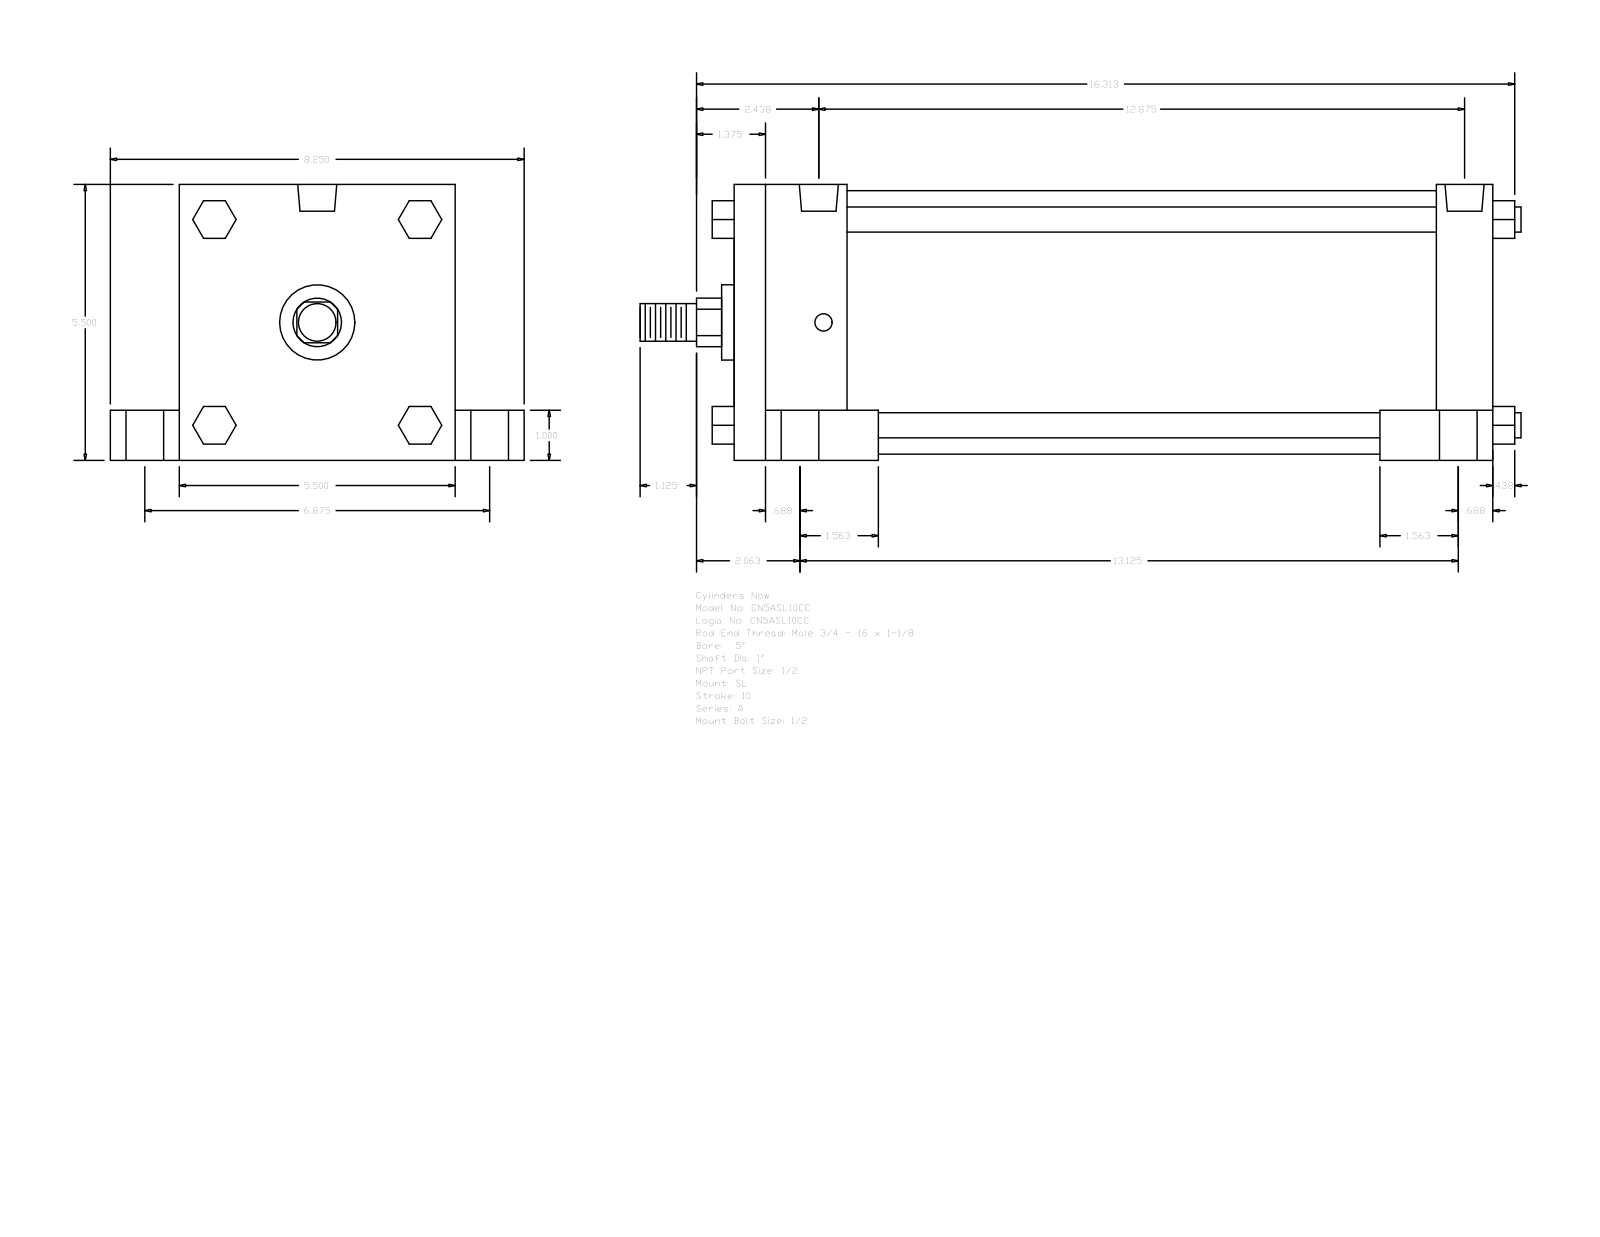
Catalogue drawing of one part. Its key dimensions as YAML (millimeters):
part_name: "A_SL__0500_1"
step_written_by: "GSSL Pune (CONFIG_CONTROL_DESIGN)"
units: millimeters
bodies: {solids: 0, faces: 150, planar: 114, cylindrical: 36, other: 0}
overall_size: [446.09, 209.55, 139.7]
round_holes:
  - {diameter: 8.73, count: 4}
  - {diameter: 19.05, count: 4}
  - {diameter: 25.4, count: 4}
  - {diameter: 19.77, count: 2}
round_bosses_or_shafts:
  - {diameter: 12.7, count: 4}
  - {diameter: 133.35, count: 1}
  - {diameter: 38.1, count: 1}
  - {diameter: 25.4, count: 1}
  - {diameter: 19.05, count: 1}
partial_cylinders:
  - {radius: 12.29, count: 1}
face_to_face_distances: [139.7, 384.18, 28.58, 25.4, 114.3, 34.93, 174.63, 57.15, 355.6, 298.45]
hole_center_spacings: [2.39, 87.31, 87.37, 87.83, 88.12, 174.62, 322.25, 324.64]
